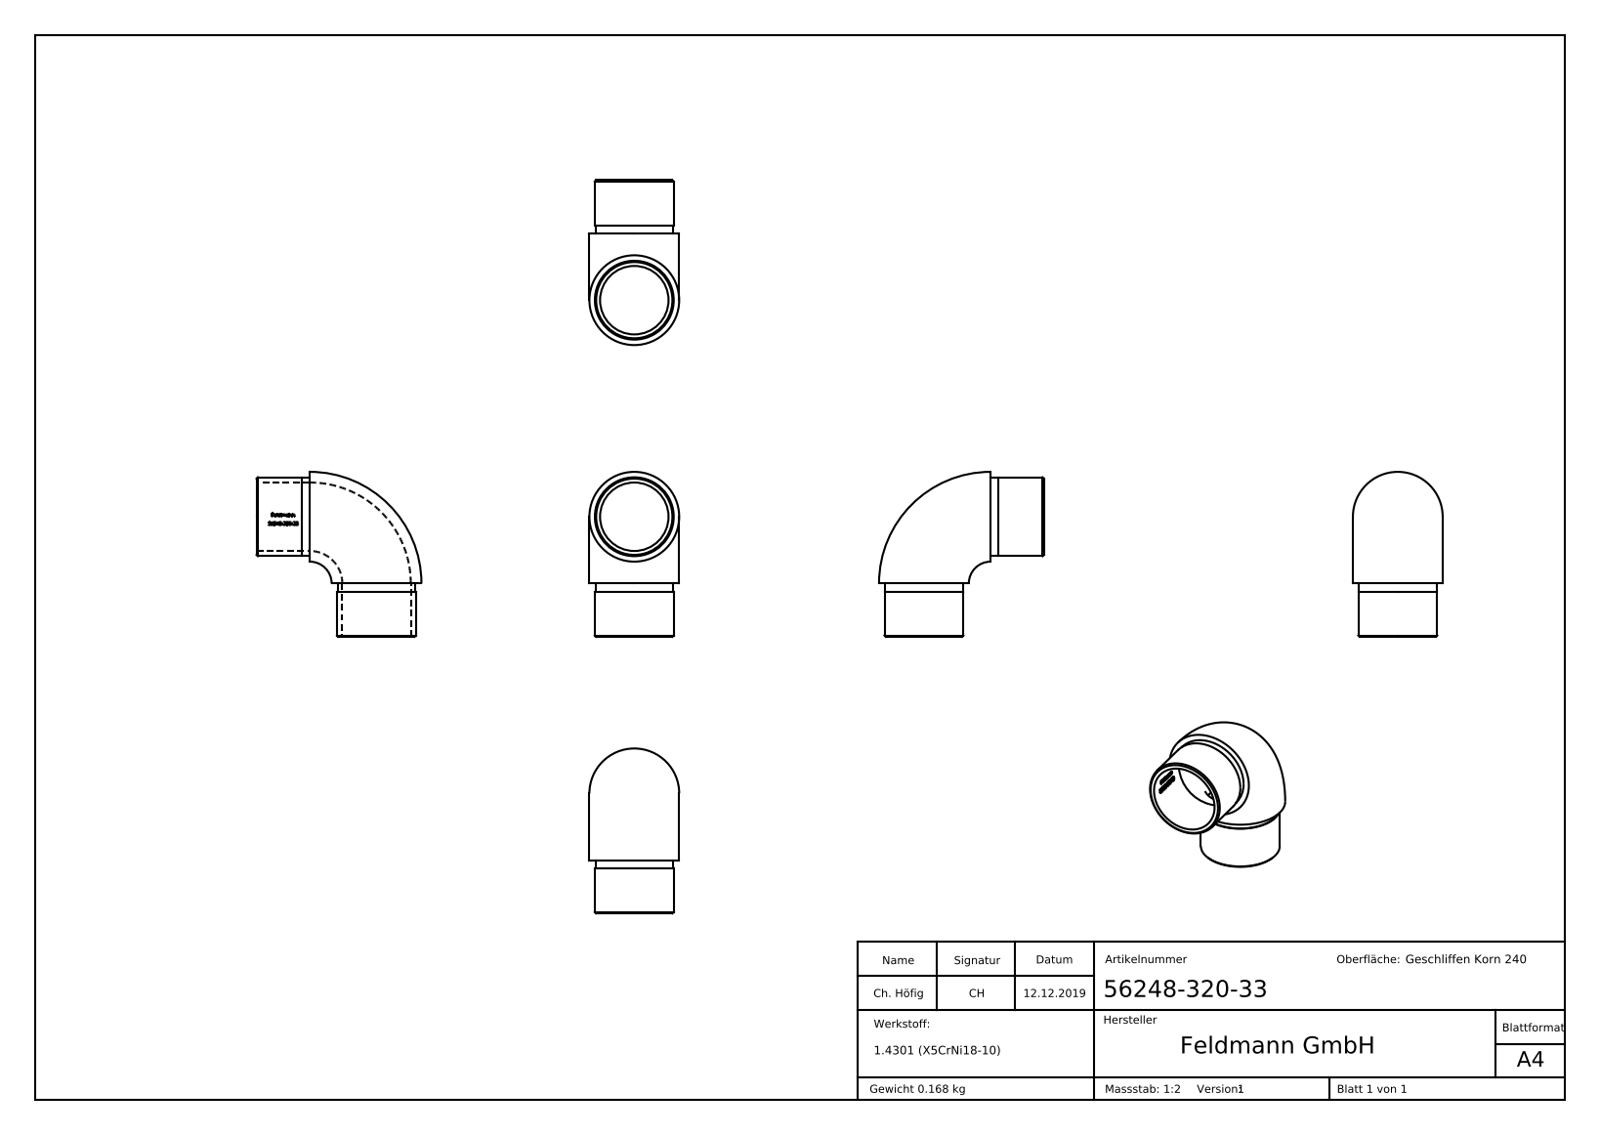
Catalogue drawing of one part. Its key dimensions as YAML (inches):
part_name: "56248-320-33"
step_written_by: "SolidWorks 2015 (CONFIG_CONTROL_DESIGN)"
units: inches
bodies: {solids: 1, faces: 294, planar: 111, cylindrical: 34, other: 149}
overall_size: [2.437, 2.437, 1.327]
volume: 1.301
surface_area: 23.42
round_holes:
  - {diameter: 1.012, count: 2}
round_bosses_or_shafts:
  - {diameter: 1.165, count: 2}
  - {diameter: 1.15, count: 2}
partial_cylinders:
  - {radius: 0.526, count: 1}
face_to_face_distances: [0.787, 0.669, 0.118, 0.117, 0.017, 0.144, 0.139, 0.129, 0.015, 0.052]
